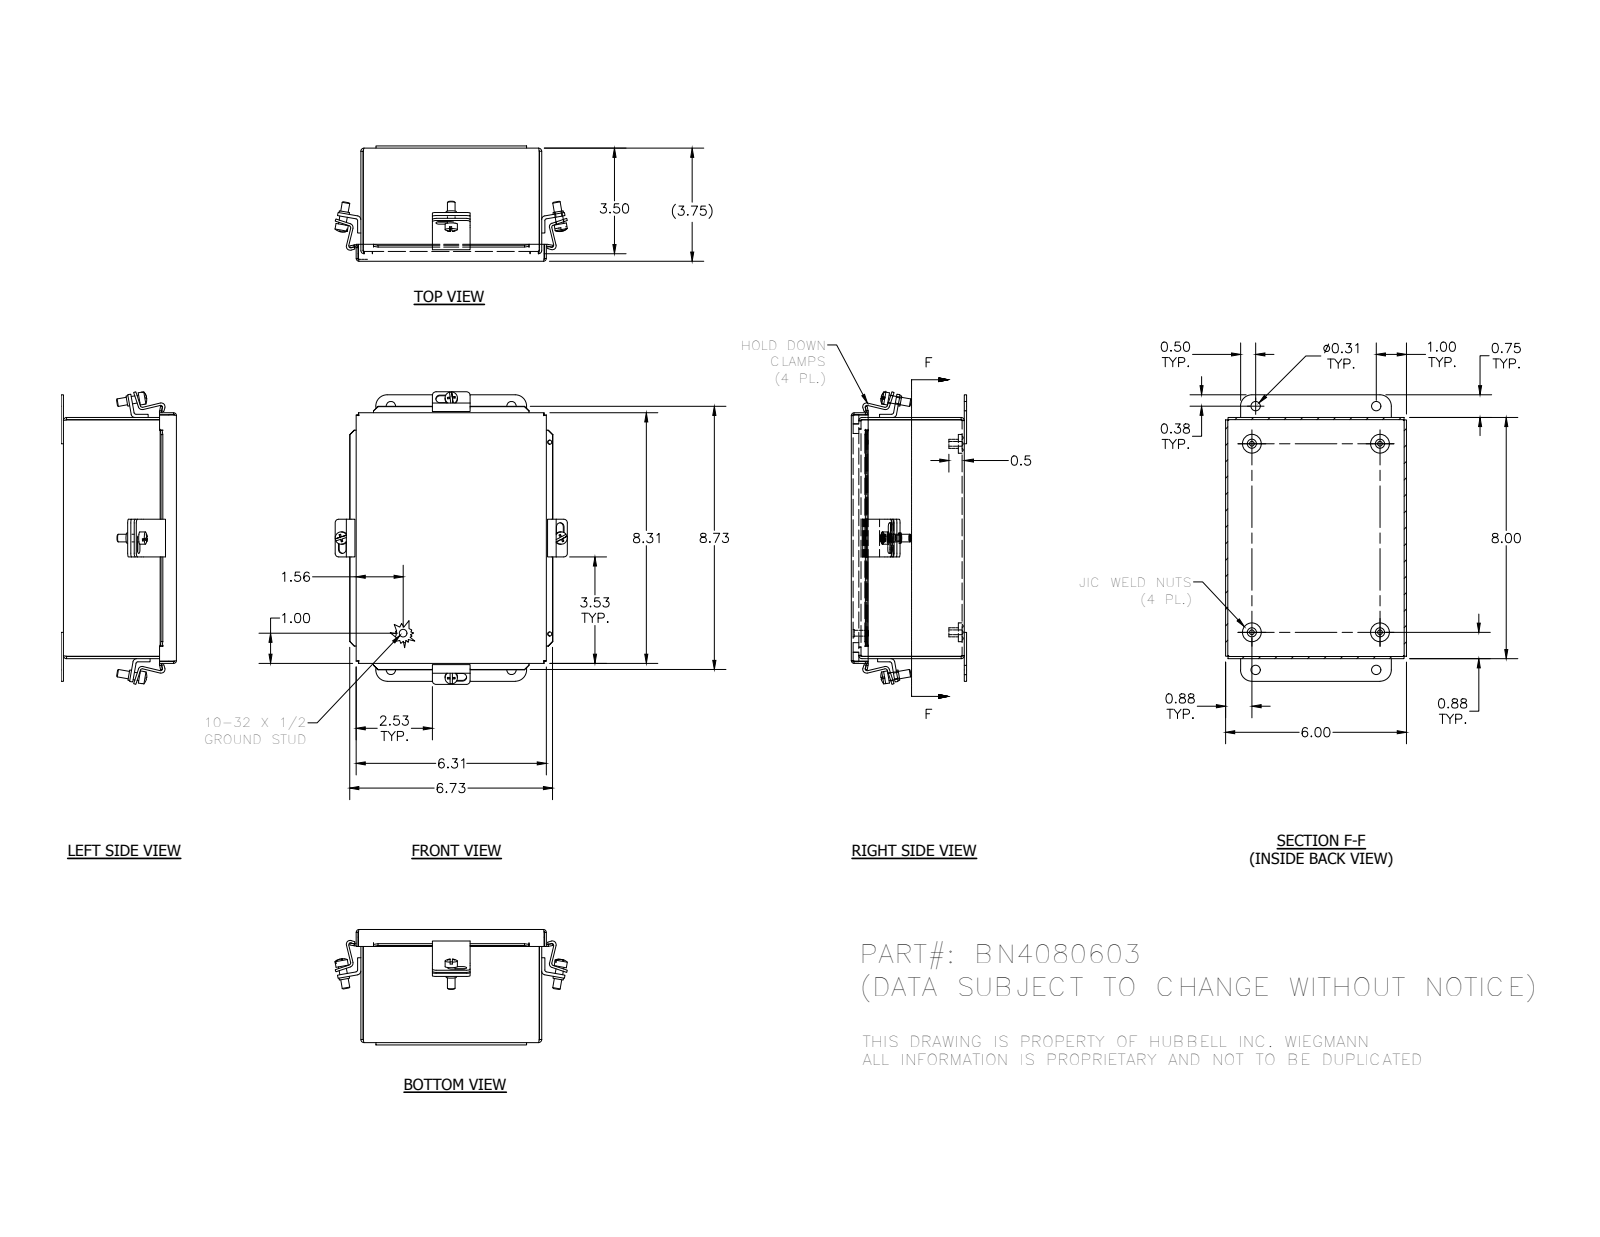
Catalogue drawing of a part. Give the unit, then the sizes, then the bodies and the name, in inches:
Units: inches
Overall size (bounding box): 9.704 × 7.705 × 3.824
Round holes (diameter × count): ⌀0.156 ×4, ⌀0.196 ×4, ⌀0.31 ×4, ⌀0.136 ×2
Round bosses / shafts (diameter × count): ⌀0.25 ×5, ⌀0.625 ×4, ⌀0.41 ×4, ⌀0.344 ×4, ⌀0.3 ×4, ⌀0.19 ×1
Partial cylindrical surfaces — rounded edges, fillets, slot ends (radius × count): R0.031 ×16, R0.125 ×16, R0.063 ×12, R0.126 ×12, R0.093 ×8, R0.105 ×8, R0.133 ×8, R0.375 ×4
Main face-to-face distances: 0.074, 3.687, 0.062, 5.926, 3.75, 3.613, 3.676, 7.926, 3.426, 6
Hole centre spacings: 1.256, 4.31, 7.501, 8.559, 4, 4.25, 6.25, 7.558
Volume: 21.23 in³ · Surface area: 561.6 in²
Bodies: 23 solids, 537 faces (295 planar, 172 cylindrical, 70 other)
Part name (STEP PRODUCT): C1001_1; 38811_1; 3499_1; 3482_1 (+6 more)
STEP written by: SolidWorks 2014 (AUTOMOTIVE_DESIGN)
